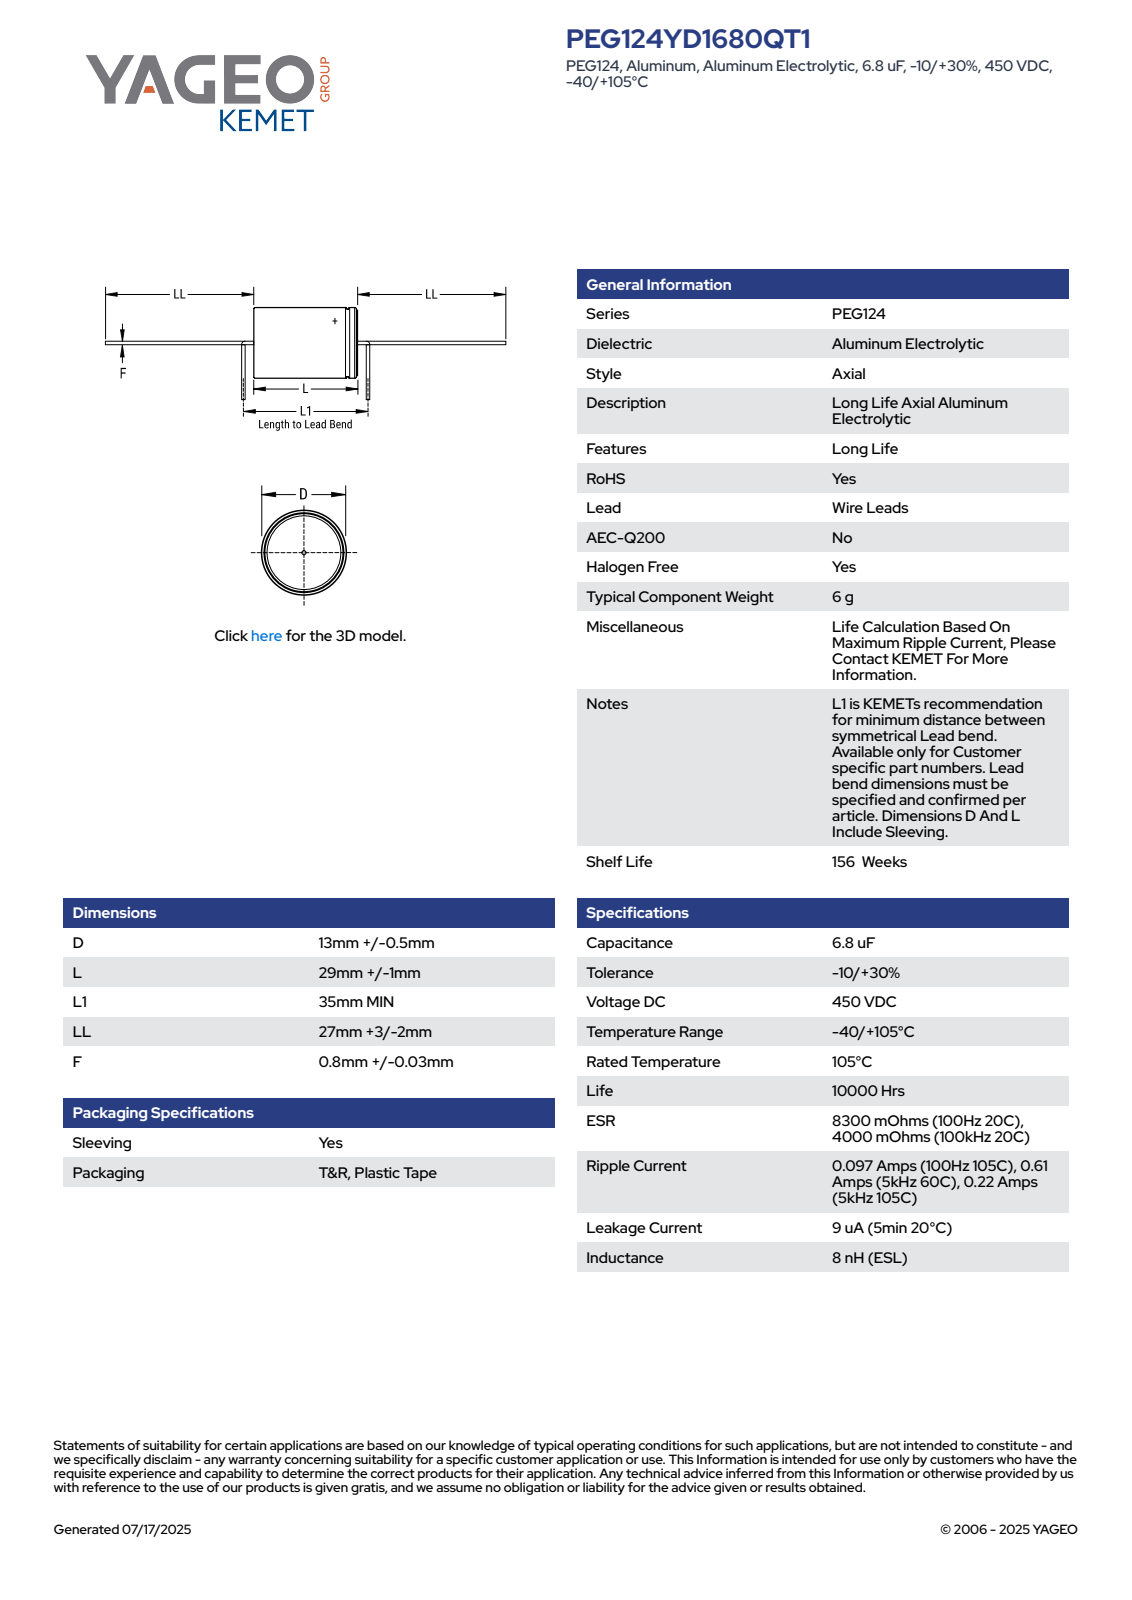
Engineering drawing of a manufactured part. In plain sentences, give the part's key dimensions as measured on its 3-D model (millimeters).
The part is named "CAA_PEG124_13X29_D13.5L30LL30F0.83". Its 3-D file was written by "SolidWorks 2014 (AUTOMOTIVE_DESIGN)". It is 1 solid with 99 faces: 27 planar, 29 cylindrical and 43 other. Overall it measures 102 by 13.5 by 13.5 millimeters. Its volume is 4 204 cubic millimeters and its surface area 1 791 square millimeters. Round holes: 1 of diameter 12.5. Round bosses or shafts: 1 of diameter 13.5, 1 of diameter 13, 1 of diameter 0.83. Partial cylindrical surfaces (rounded edges, fillets, slot ends): 1 of radius 6.74. The main face-to-face distances are 29, 30, 1, 59, 60, 102, 72, 43, 42.
